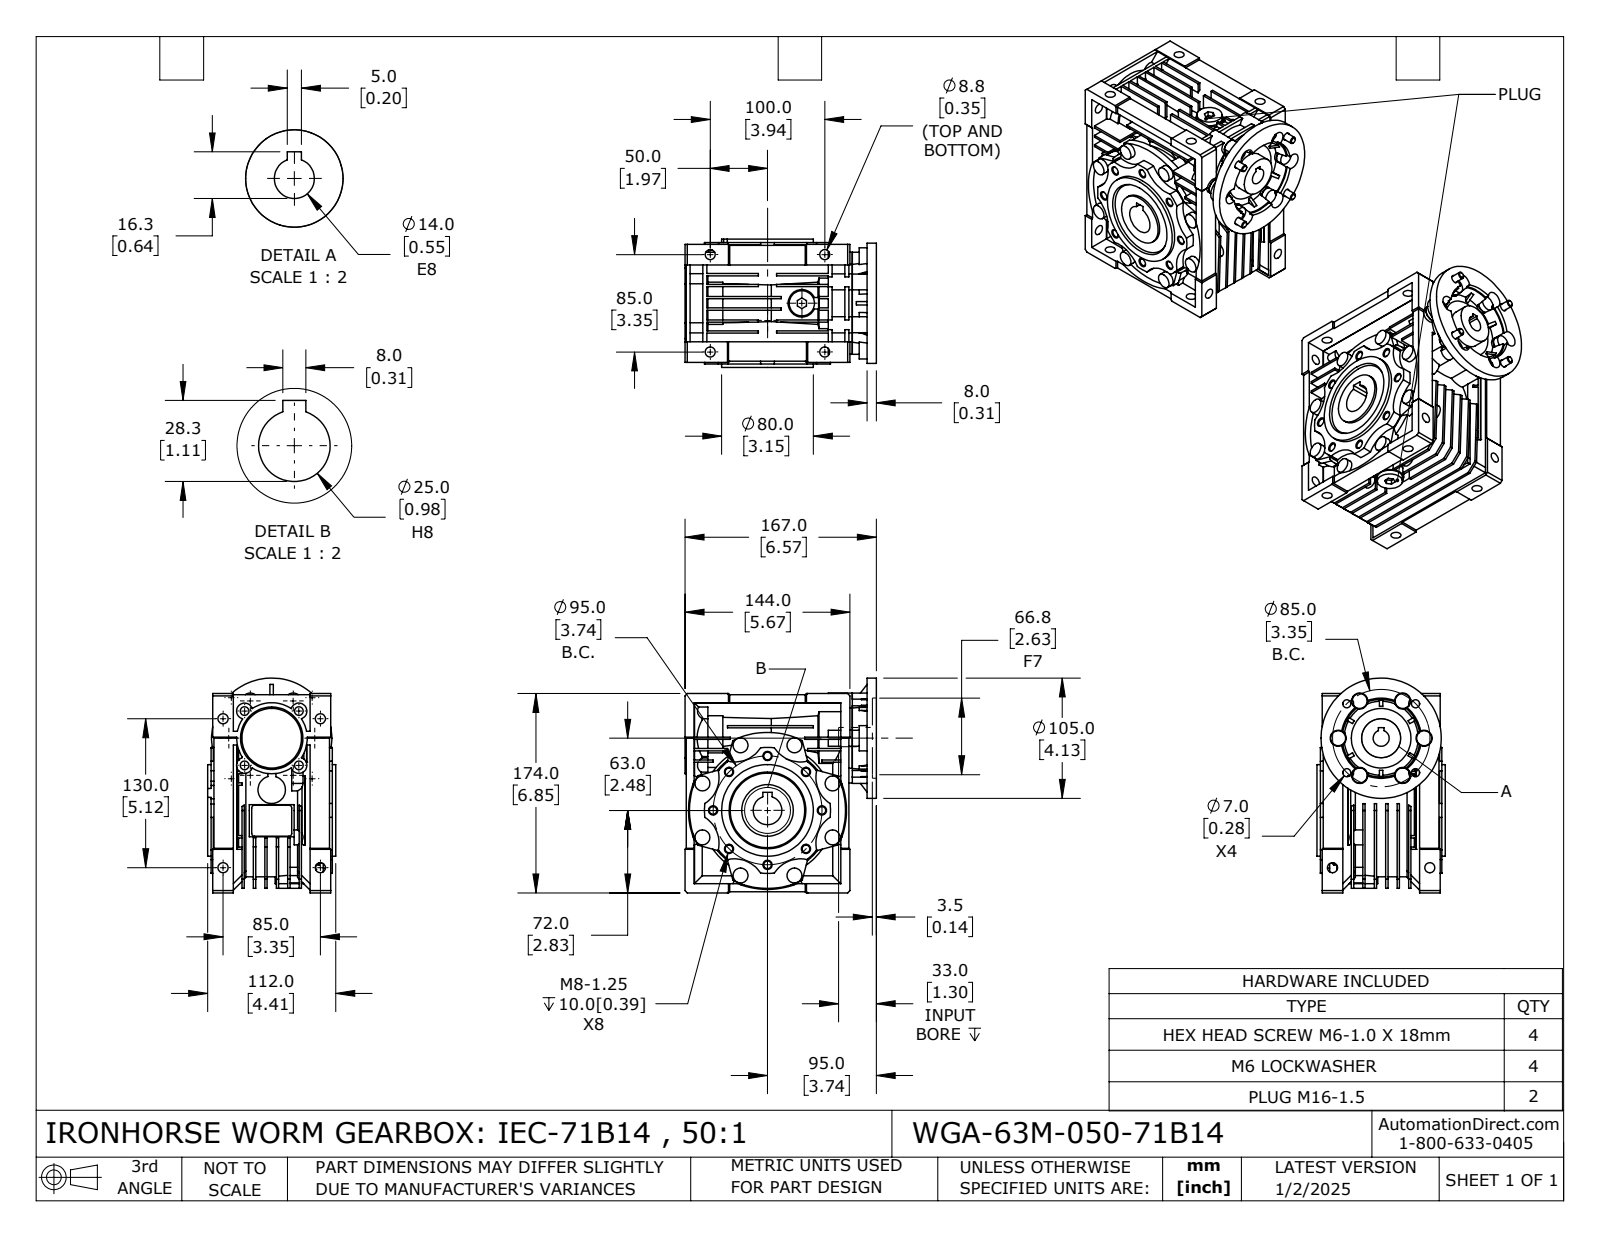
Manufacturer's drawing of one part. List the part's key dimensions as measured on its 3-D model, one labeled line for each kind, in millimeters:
Part name (STEP PRODUCT): WGA-63M-050-71B14
STEP written by: SolidWorks 2024 (CONFIG_CONTROL_DESIGN)
Units: millimetres
Bodies: 16 solids, 1428 faces (836 planar, 417 cylindrical, 175 other)
Overall size (bounding box): 187.5 × 175.5 × 112
Volume: 1 817 000 mm³ · Surface area: 341 752 mm²
Round holes (diameter × count): ⌀6.65 ×8, ⌀8.78 ×8, ⌀6.1 ×4, ⌀7 ×4, ⌀7.56 ×4, ⌀14.5 ×2, ⌀14 ×1, ⌀15 ×1, ⌀25 ×1, ⌀34 ×1, ⌀37 ×1, ⌀45 ×1
Round bosses / shafts (diameter × count): ⌀13 ×14, ⌀14 ×4, ⌀12.2 ×4, ⌀6 ×4, ⌀24 ×3, ⌀22 ×2, ⌀15.8 ×2, ⌀13.7 ×2
Partial cylindrical surfaces — rounded edges, fillets, slot ends (radius × count): R7 ×12, R27 ×8, R6.98 ×6, R11 ×6, R2.5 ×4, R6 ×4, R8.35 ×1, R29.5 ×1
Main face-to-face distances: 10, 8, 20, 2, 30, 7, 12, 40, 18, 1
Hole centre spacings: 36.36, 47.5, 54.12, 67.18, 87.77, 8.99, 33.5, 42.5
